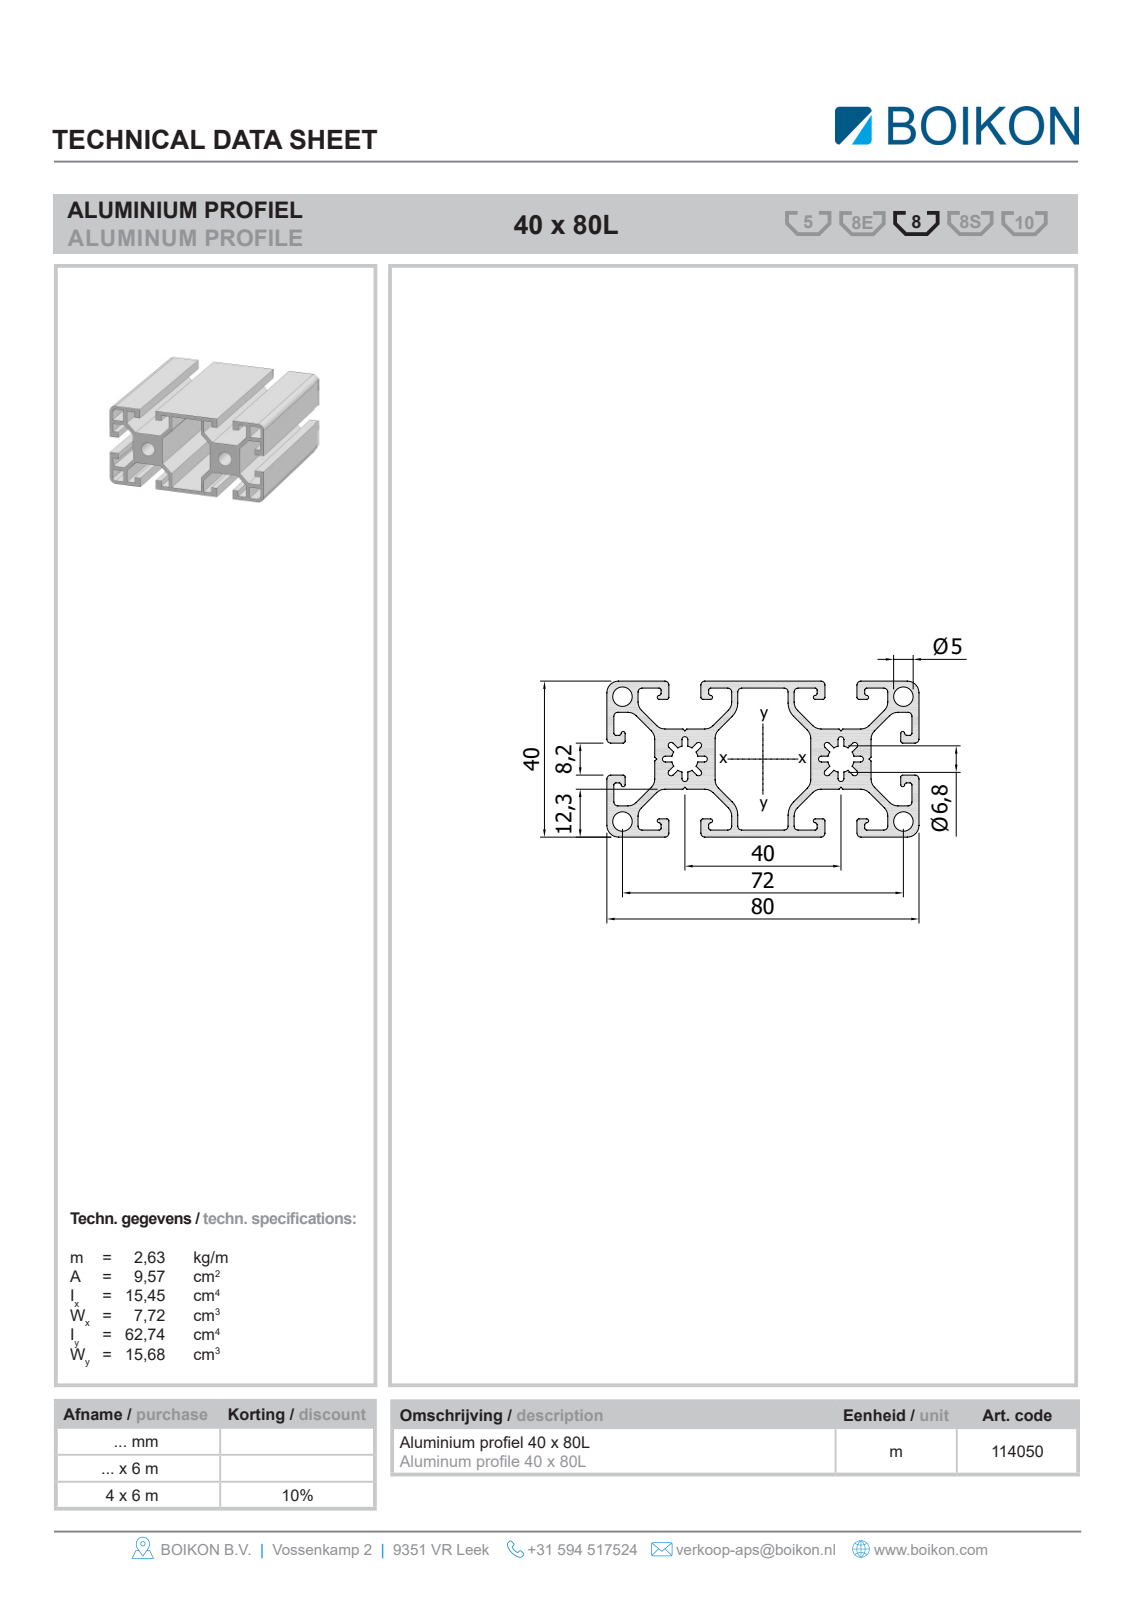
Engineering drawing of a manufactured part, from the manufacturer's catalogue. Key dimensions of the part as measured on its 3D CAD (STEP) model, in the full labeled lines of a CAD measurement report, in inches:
Part name (STEP PRODUCT): Root; 11405040x80LBOIKON0
STEP written by: HiCAD 2013 1802.4 Build 509 (AUTOMOTIVE_DESIGN)
Units: inches
Bodies: 1 solid, 128 faces (118 planar, 10 cylindrical, 0 other)
Overall size (bounding box): 39.37 × 3.15 × 1.575
Volume: 61.7 in³ · Surface area: 1 279 in²
Round holes (diameter × count): ⌀0.268 ×2
Partial cylindrical surfaces — rounded edges, fillets, slot ends (radius × count): R0.059 ×4, R0.118 ×4
Main face-to-face distances: 0.071, 1.575, 1.22, 1.091, 0.484, 0.13, 0.736, 0.283, 1.504, 0.272
Hole centre spacings: 1.575
